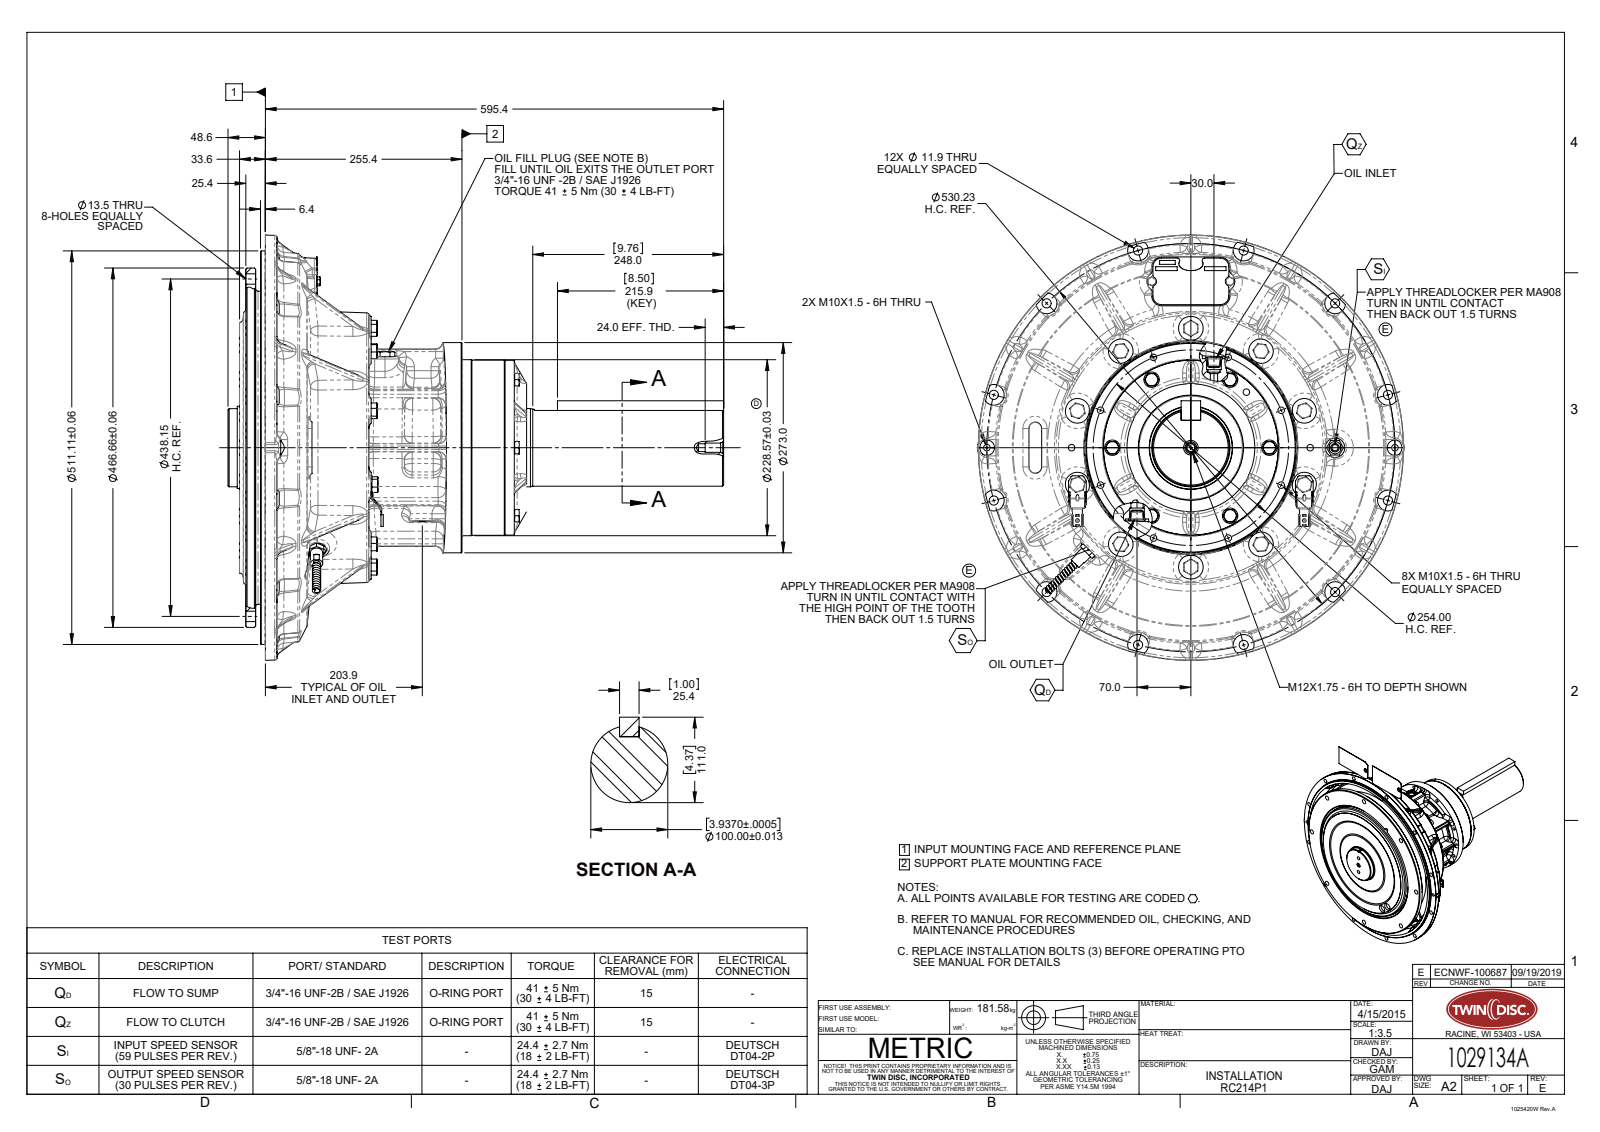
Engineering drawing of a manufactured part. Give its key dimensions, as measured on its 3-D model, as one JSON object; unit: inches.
{"part_name": "1029134A", "step_written_by": "SolidWorks 2019 (AUTOMOTIVE_DESIGN)", "units": "inches", "bodies": {"solids": 0, "faces": 1855, "planar": 426, "cylindrical": 357, "other": 1072}, "overall_size": [25.354, 21.813, 21.744], "round_holes": [[0.335, 14], [0.468, 10], [0.531, 8], [1.188, 3], [0.187, 2], [0.402, 2], [0.468, 2], [0.75, 2], [0.875, 2], [1, 2], [0.425, 1], [0.472, 1]], "round_bosses_or_shafts": [[0.625, 2], [0.315, 2], [20.123, 1], [18.373, 1], [10.866, 1], [10.748, 1], [8.999, 1], [8.957, 1]], "partial_cylinders_radius": [[0.394, 96], [0.118, 76], [0.197, 12], [0.531, 12], [0.06, 6], [0.44, 4], [0.5, 4], [0.09, 3]], "face_to_face_distances": [0.715, 1, 0.285, 1.326, 0.61, 0.326, 1.267, 0.551, 0.267, 0.059], "hole_center_spacings": [8.148, 11.506, 4.439, 13.382, 3.827, 5, 6.601, 7.071]}
